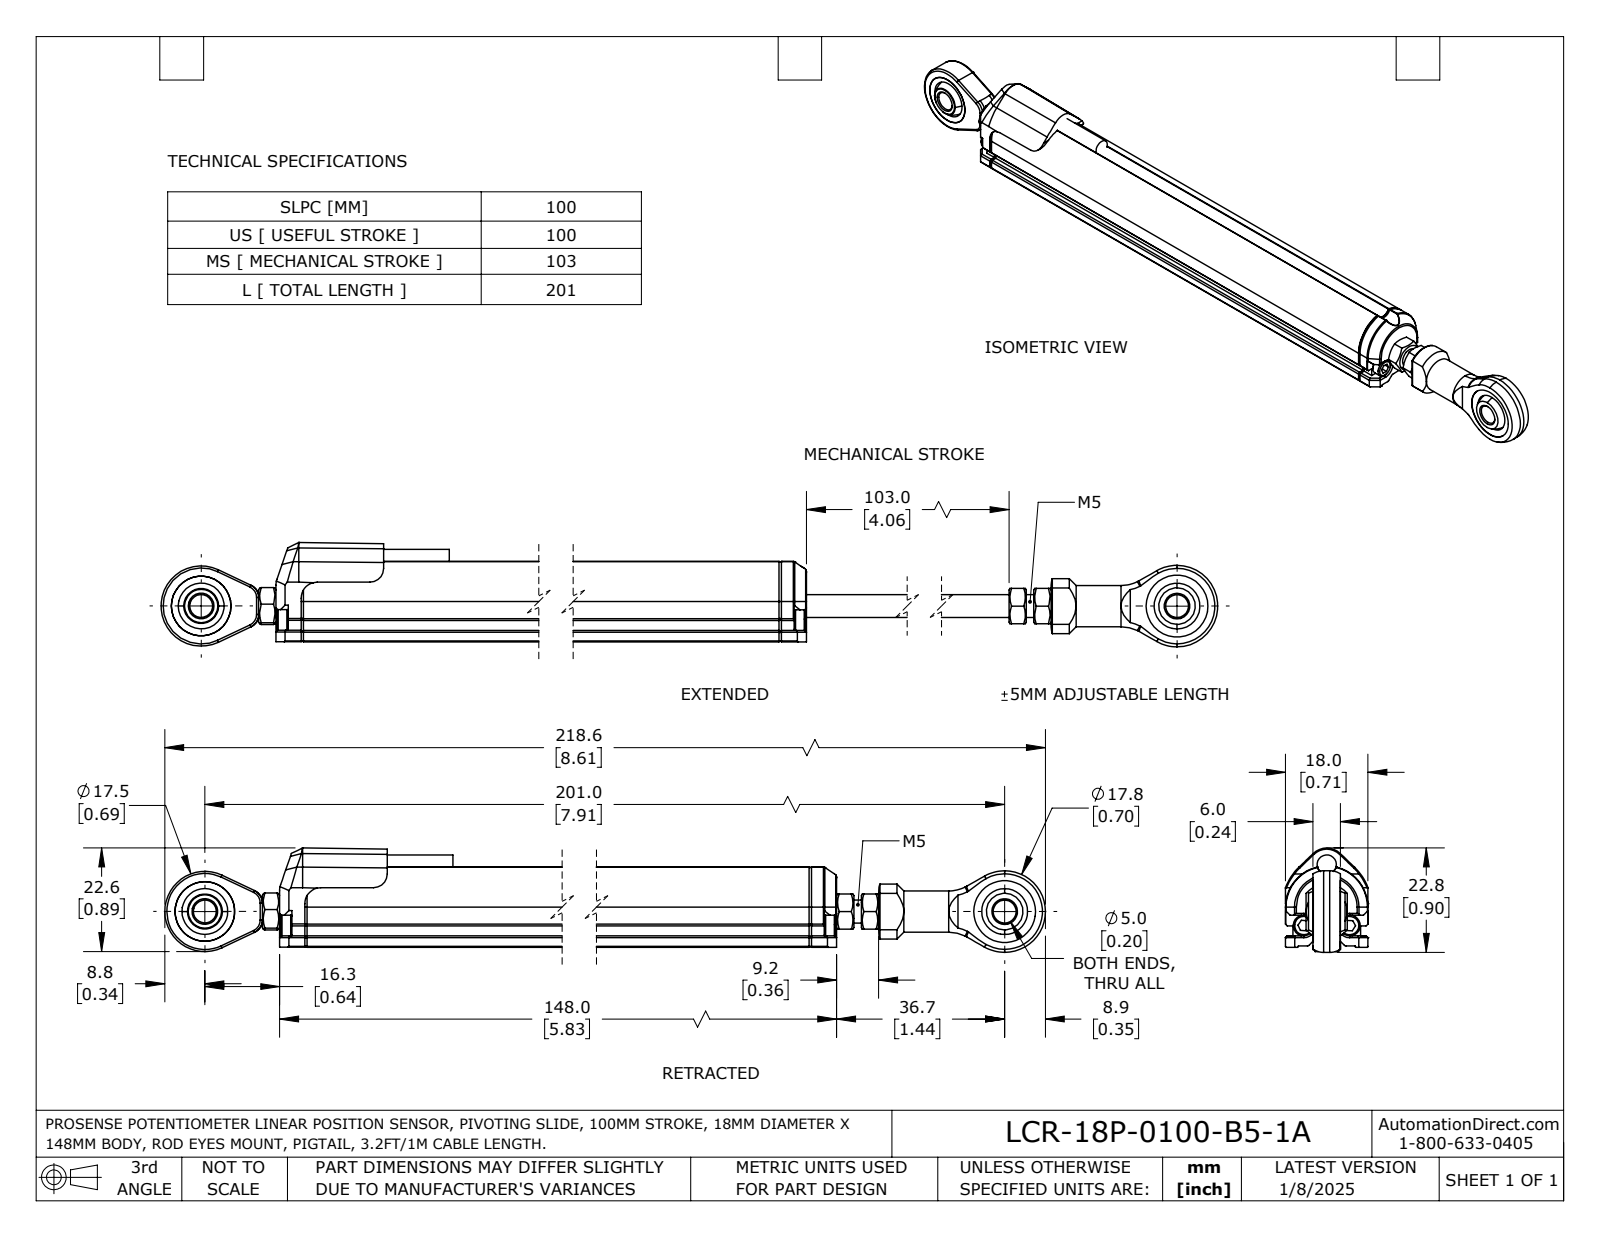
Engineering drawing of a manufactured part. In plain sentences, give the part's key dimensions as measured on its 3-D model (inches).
The part is named "LCR-18P-0100-B5-1A". Its 3-D file was written by "SolidWorks 2023 (AUTOMOTIVE_DESIGN)". It is 20 solids with 515 faces: 289 planar, 136 cylindrical and 90 other. Overall it measures 8.608 by 0.896 by 0.709 inches. Its volume is 2.764 cubic inches and its surface area 34.15 square inches. Round holes: 4 of diameter 0.197, 2 of diameter 0.102, 2 of diameter 0.104, 2 of diameter 0.394, 1 of diameter 0.213, 1 of diameter 0.272, 1 of diameter 0.512, 1 of diameter 0.531. Round bosses or shafts: 4 of diameter 0.181, 3 of diameter 0.113, 2 of diameter 0.059, 1 of diameter 0.354, 1 of diameter 0.165, 1 of diameter 0.113. Partial cylindrical surfaces (rounded edges, fillets, slot ends): 12 of radius 0.008, 10 of radius 0.004, 8 of radius 0.02, 6 of radius 0.012, 6 of radius 0.018, 4 of radius 0.016, 4 of radius 0.039, 4 of radius 0.043. The main face-to-face distances are 0.02, 5.374, 0.236, 0.709, 0.059, 0.071, 0.063, 0.646, 5.354, 0.173. The hole center spacings are 0.231, 0.394, 0.23, 0.231, 7.913.
